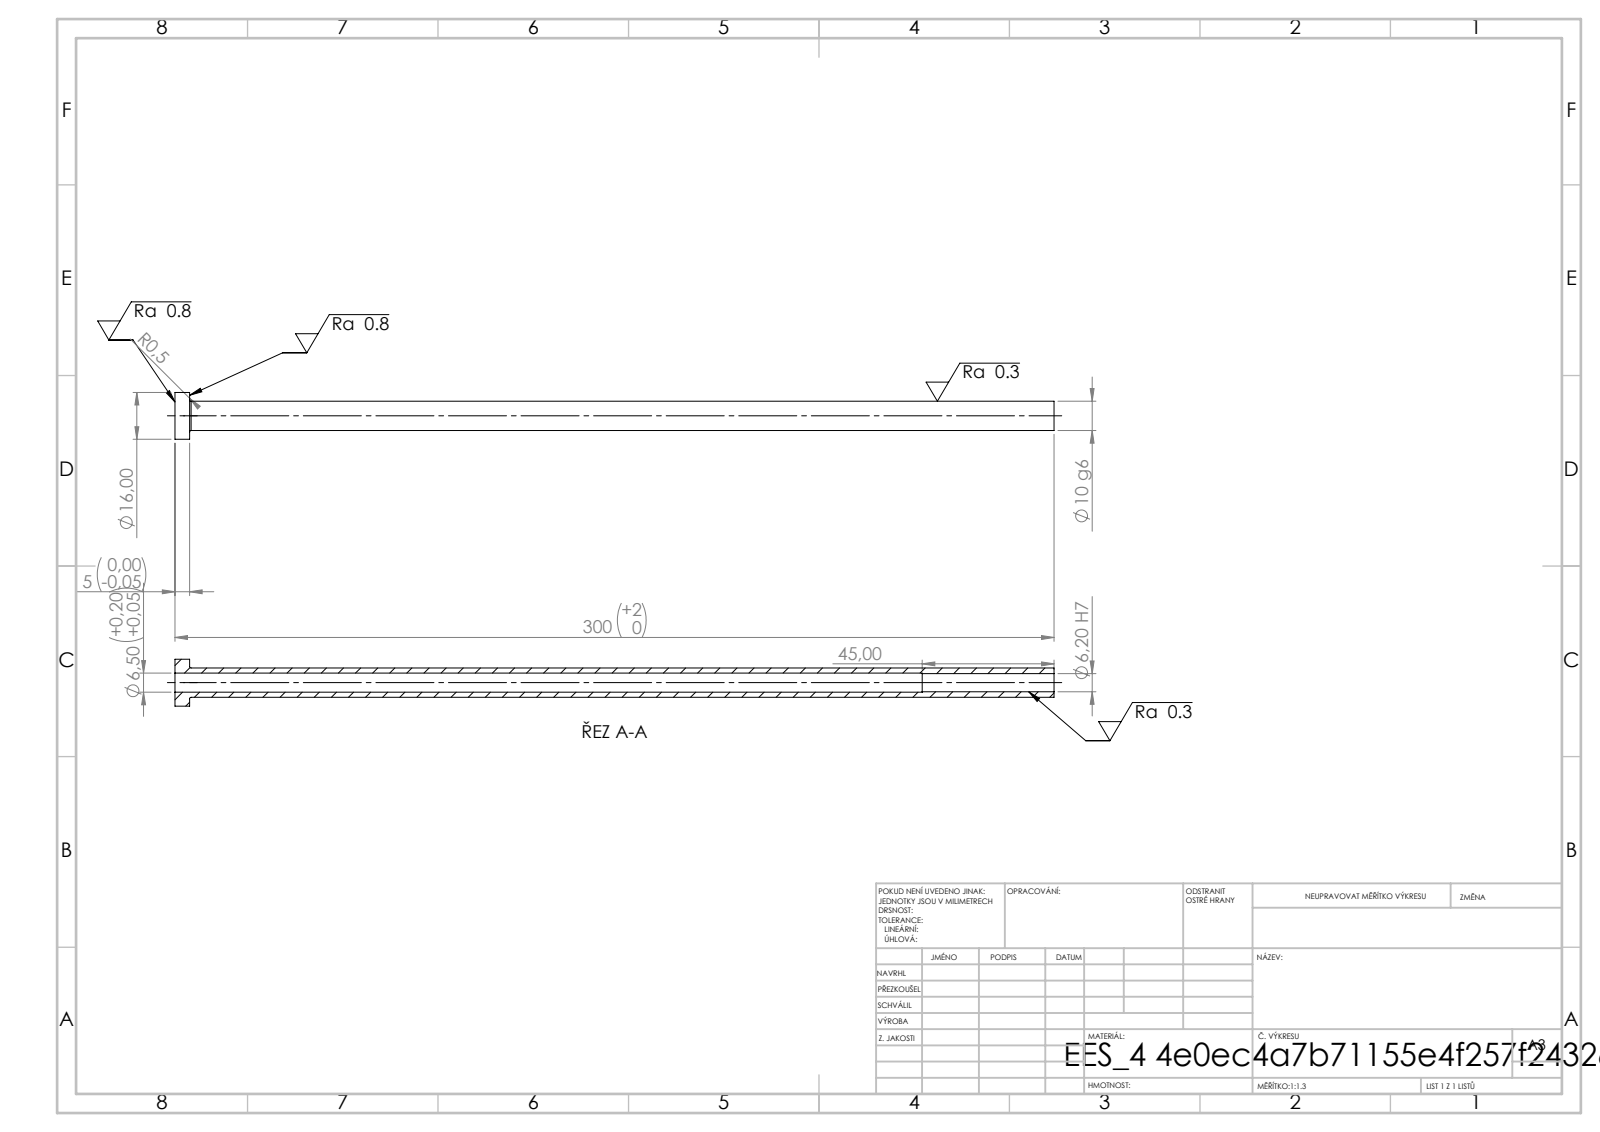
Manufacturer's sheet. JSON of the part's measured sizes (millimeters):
{"step_written_by": "SolidWorks 2019 (CONFIG_CONTROL_DESIGN)", "units": "millimeters", "bodies": {"solids": 1, "faces": 14, "planar": 4, "cylindrical": 8, "other": 2}, "overall_size": [300, 16, 16], "volume_mm3": 14356, "surface_area_mm2": 15938, "round_holes": [[6.2, 1], [6.5, 1]], "round_bosses_or_shafts": [[16, 1], [10, 1]], "face_to_face_distances": [5, 300, 295, 255, 250, 45]}
